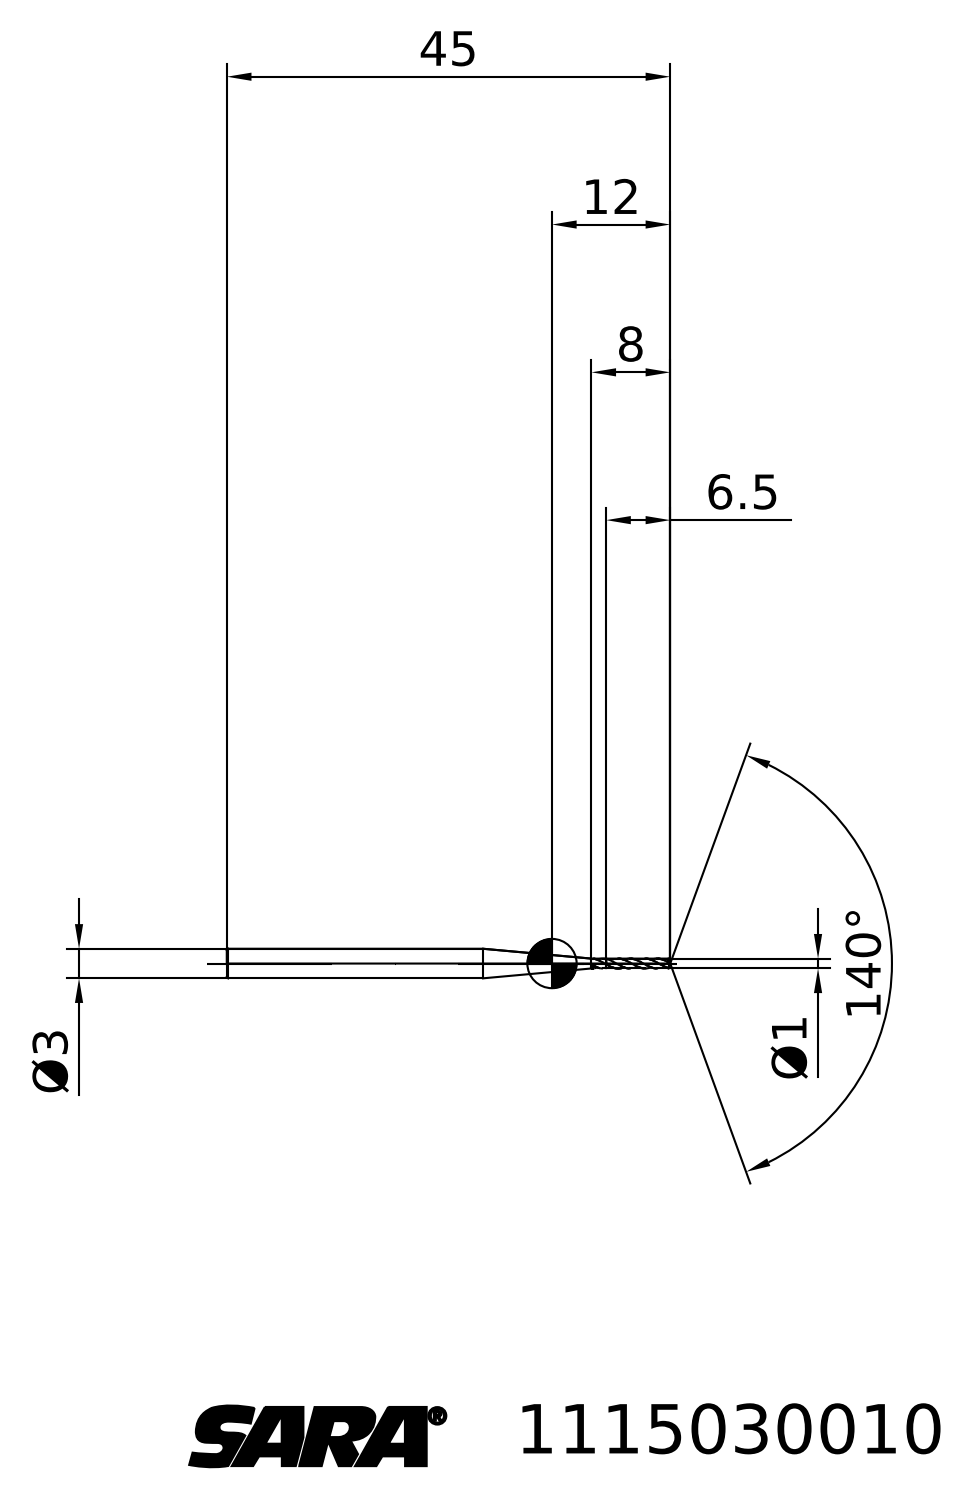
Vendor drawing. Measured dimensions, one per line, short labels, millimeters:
written by: TDM (AUTOMOTIVE_DESIGN)
unit: mm
bodies: 2 solids, 28 faces (3 planar, 0 cylindrical, 25 other)
size: 45 × 3 × 3
volume: 225 mm³; area: 349 mm²
face distances: 38.5
